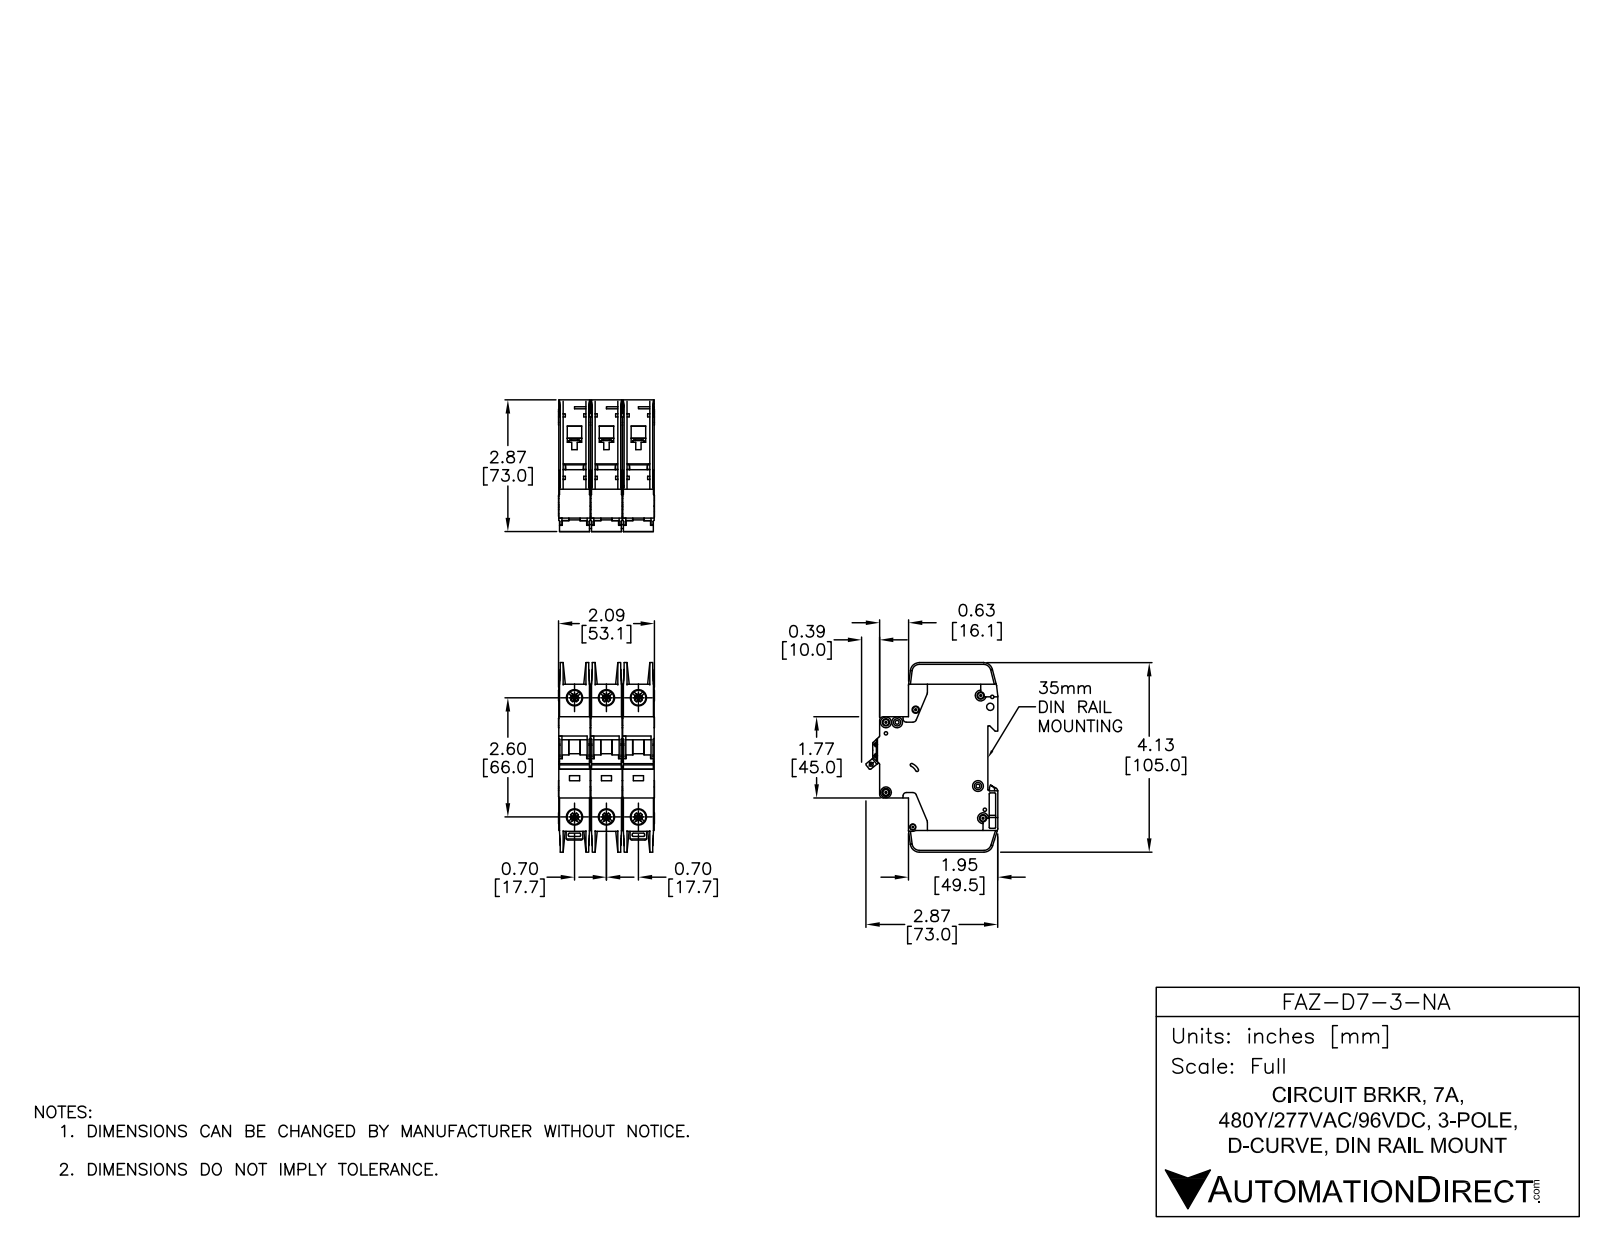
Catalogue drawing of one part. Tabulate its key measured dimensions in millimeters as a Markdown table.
| quantity | value |
| --- | --- |
| part name | FAZ-D7-3-NA |
| STEP written by | SolidWorks 2014 (AUTOMOTIVE_DESIGN) |
| units | millimeters |
| bodies | 9 solids, 2352 faces (1227 planar, 789 cylindrical, 336 other) |
| overall size | 105 × 73.04 × 53.1 |
| volume | 233 085 mm³ |
| surface area | 74 219 mm² |
| round holes (diameter × count) | 3.6 × 7, 7.15 × 6, 8.2 × 6, 1.09 × 2, 1.5 × 2, 4 × 2, 1.9 × 1, 2.15 × 1, 2.2 × 1, 2.55 × 1, 3.3 × 1, 3.4 × 1 |
| round bosses / shafts (diameter × count) | 6 × 7, 2.5 × 3 |
| partial cylindrical surfaces (radius × count) | 0.25 × 65, 0.5 × 30, 1 × 26, 2 × 14, 1.8 × 5, 5 × 5, 4 × 4, 0.2 × 2 |
| main face-to-face distances | 17.7, 35.4, 17.5, 35.2, 0.7, 15.05, 2.45, 1.75, 15.75, 13.3 |
| hole center spacings | 17.7, 68.33, 66, 6.2, 35.4, 74.89, 5.19, 6.1 |
